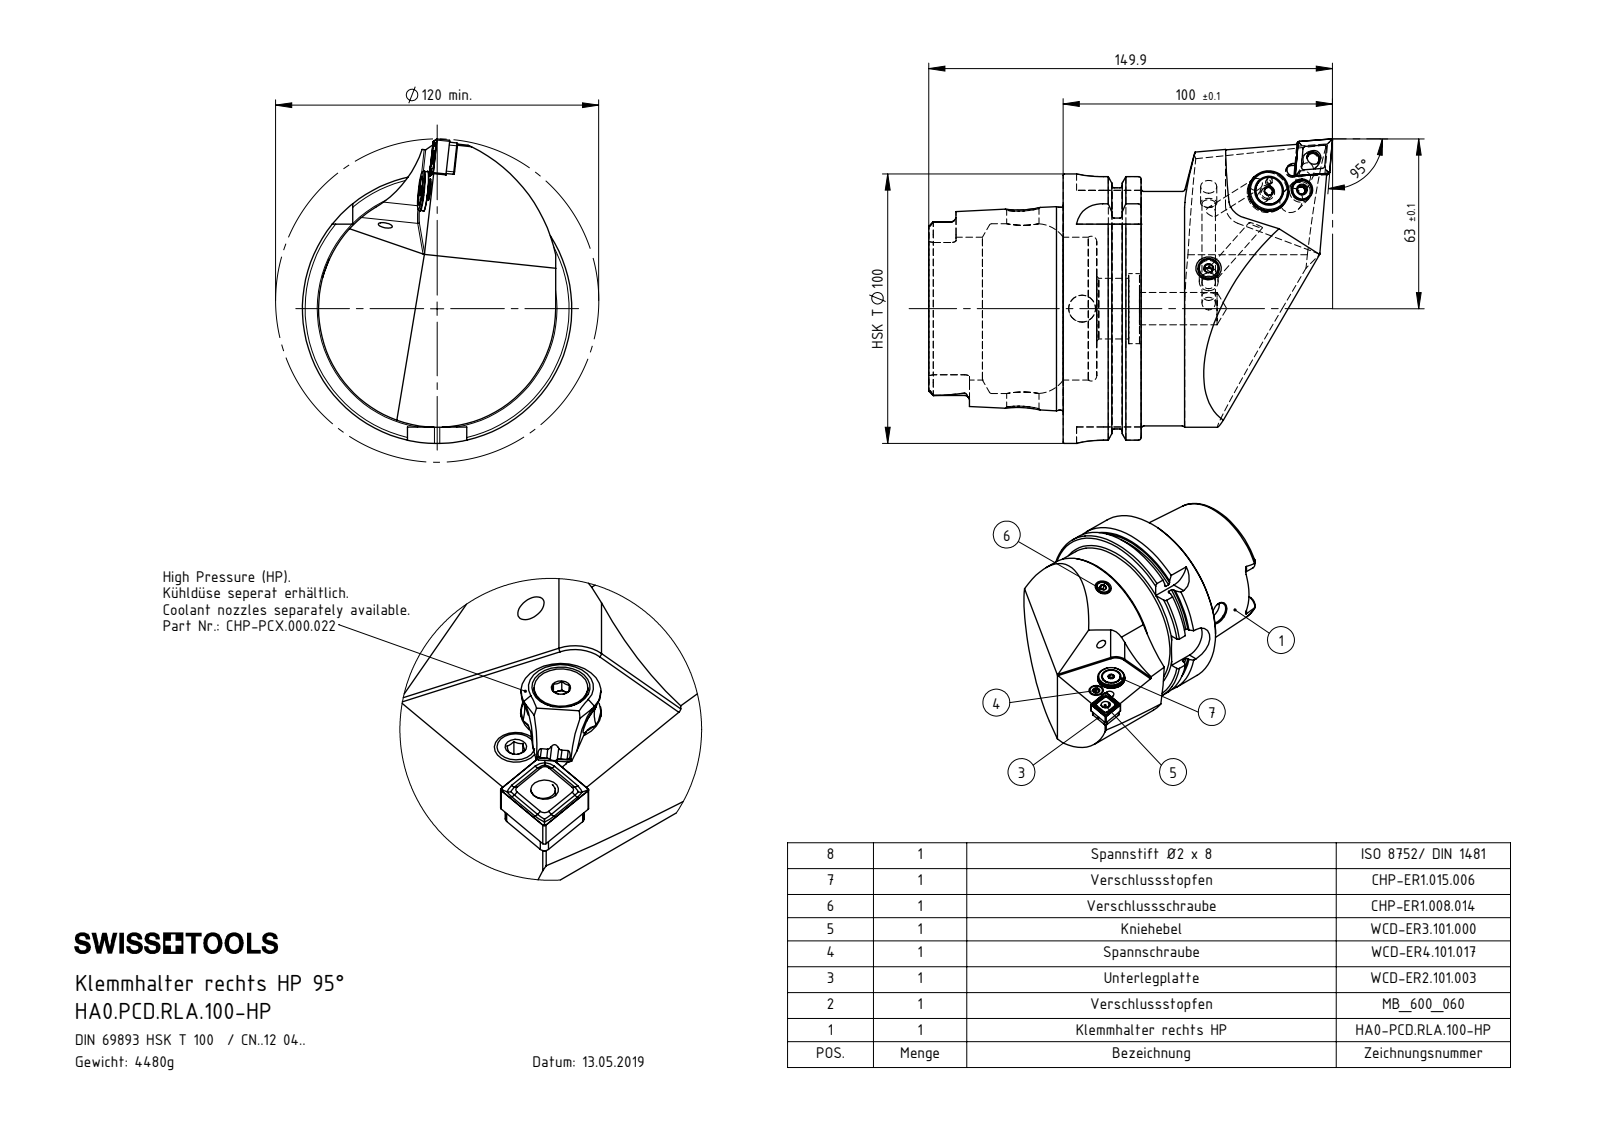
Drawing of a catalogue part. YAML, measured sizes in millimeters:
part_name: "WCD-ER2.101.003_A; PC..RLA.100-HP; CHP-ER1.015.006; DIN 3771 - 13x1 (+8 more)"
step_written_by: "SolidWorks 2022 (AUTOMOTIVE_DESIGN)"
units: millimeters
bodies: {solids: 12, faces: 511, planar: 155, cylindrical: 146, other: 210}
overall_size: [149.9, 113, 100]
volume: 570263
surface_area: 74825
round_holes:
  - {diameter: 5, count: 4}
  - {diameter: 4.2, count: 2}
  - {diameter: 7, count: 2}
  - {diameter: 12, count: 2}
  - {diameter: 1.2, count: 1}
  - {diameter: 2, count: 1}
  - {diameter: 2.5, count: 1}
  - {diameter: 3, count: 1}
  - {diameter: 5.16, count: 1}
  - {diameter: 5.2, count: 1}
  - {diameter: 6, count: 1}
  - {diameter: 6.55, count: 1}
round_bosses_or_shafts:
  - {diameter: 8, count: 2}
  - {diameter: 100, count: 1}
  - {diameter: 91.95, count: 1}
  - {diameter: 87, count: 1}
  - {diameter: 75.26, count: 1}
  - {diameter: 15, count: 1}
  - {diameter: 13.4, count: 1}
  - {diameter: 10, count: 1}
partial_cylinders:
  - {radius: 1.9, count: 6}
  - {radius: 0.4, count: 4}
  - {radius: 1, count: 4}
  - {radius: 10, count: 4}
  - {radius: 0.5, count: 2}
  - {radius: 2.5, count: 2}
  - {radius: 4.83, count: 2}
  - {radius: 4.88, count: 2}
face_to_face_distances: [12.45, 28.95, 16.5, 49.9, 62.35, 78.85, 87.8, 78.2, 28.3, 15.85]
hole_center_spacings: [4.5, 12.19, 12.53, 18.12, 18.19, 21.24, 21.32, 4.51]
